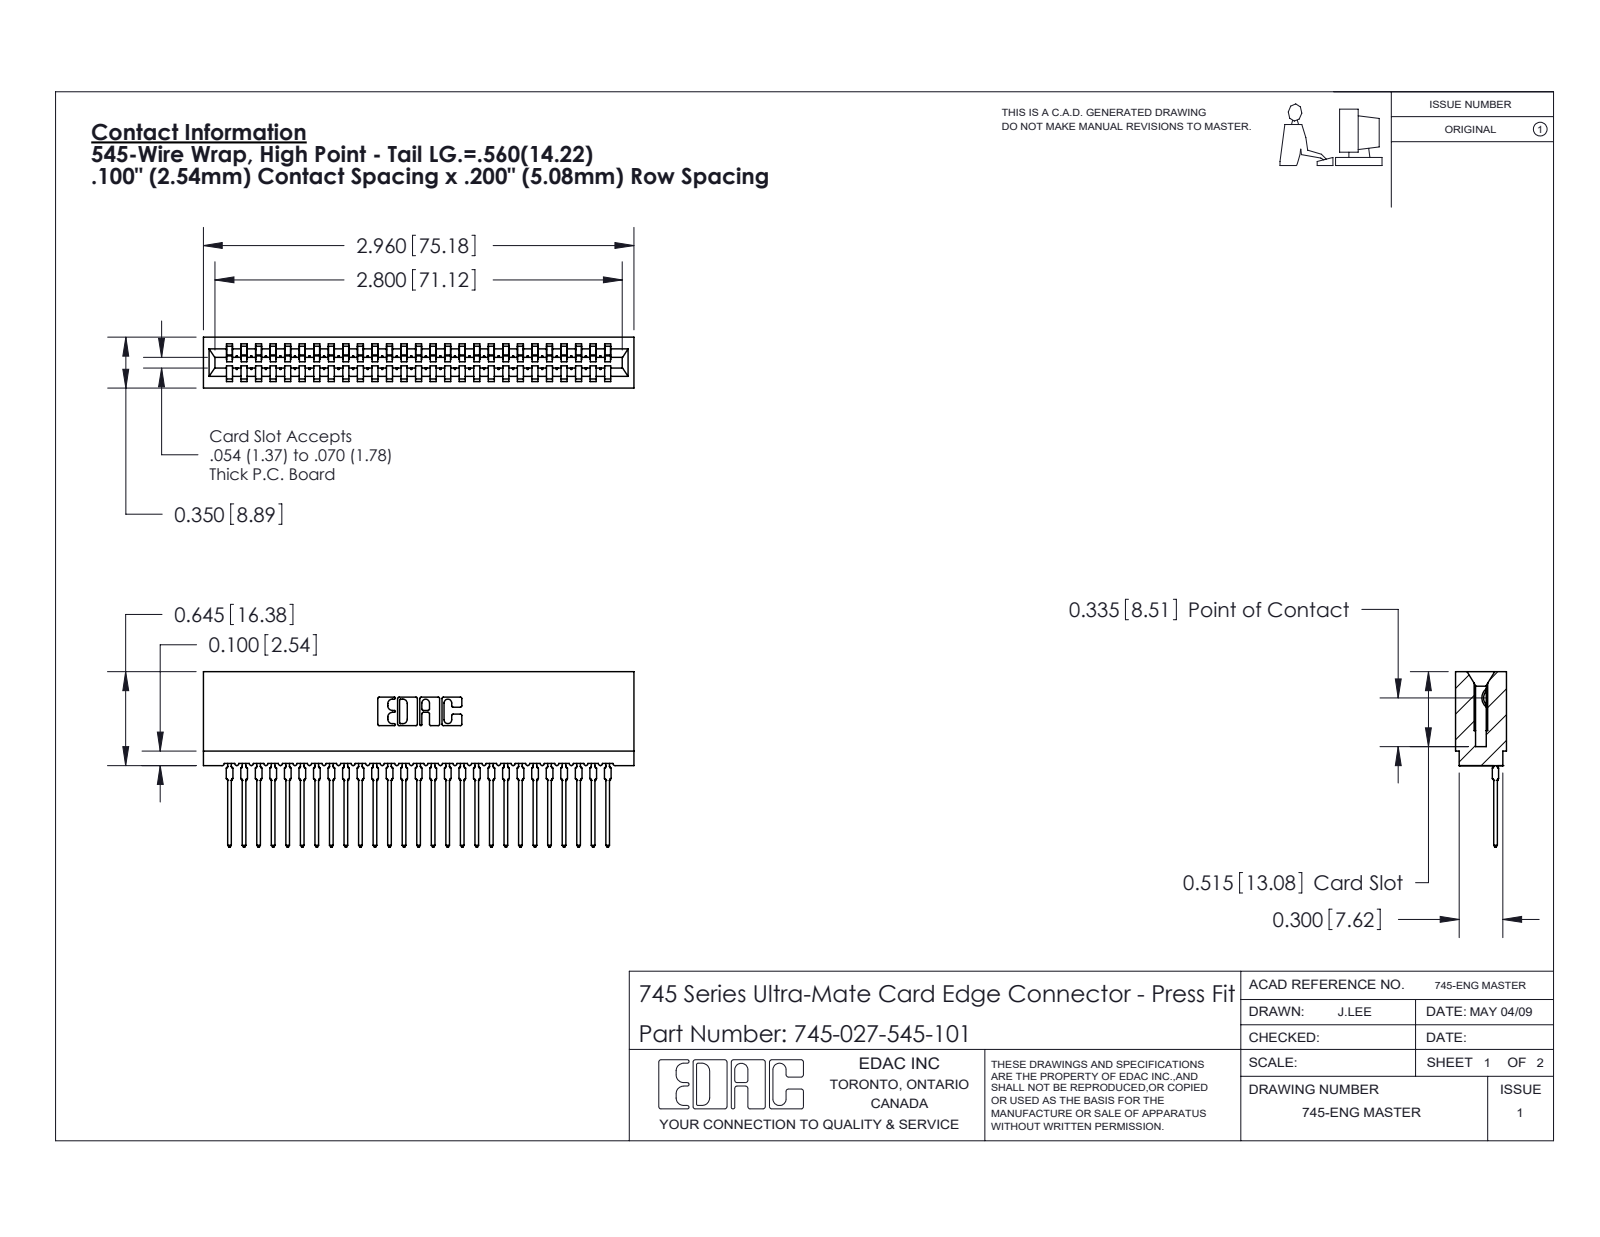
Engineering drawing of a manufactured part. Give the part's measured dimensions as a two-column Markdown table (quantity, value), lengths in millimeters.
| quantity | value |
| --- | --- |
| part name | 745-027-545-101; 745-292-001_545; 745 Part_Insulator Option - 01 |
| STEP written by | SolidWorks 2020 (CONFIG_CONTROL_DESIGN) |
| units | millimeters |
| bodies | 28 solids, 3119 faces (1864 planar, 553 cylindrical, 702 other) |
| overall size | 75.2 × 30.6 × 8.9 |
| volume | 6 690 mm³ |
| surface area | 12 570 mm² |
| partial cylindrical surfaces (radius × count) | 0.4 × 54, 0.5 × 54, 0.3 × 22, 0.2 × 6, 0.8 × 6, 0.1 × 4, 0.3 × 4, 0.7 × 3 |
| main face-to-face distances | 2.5, 8.9, 5.1, 3.5, 5.4, 1.1, 7.7, 2.4, 4.2, 1.6 |
